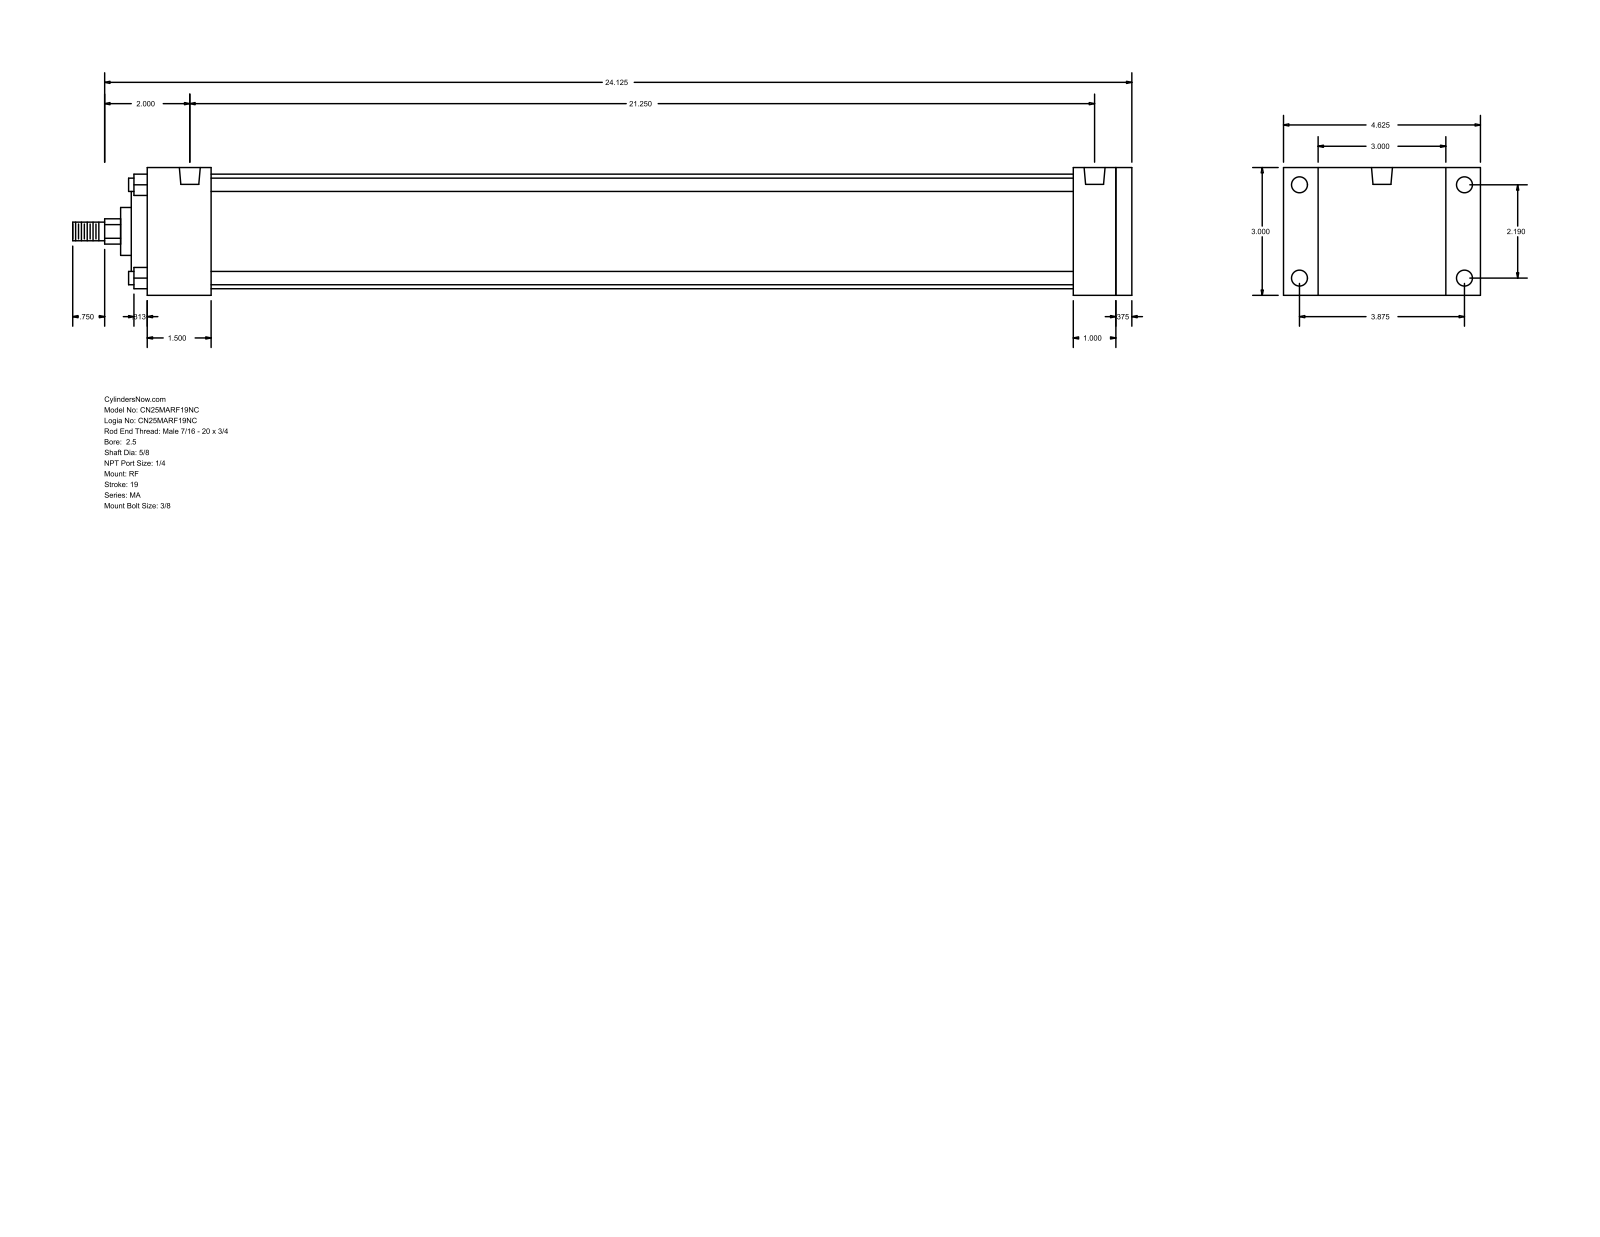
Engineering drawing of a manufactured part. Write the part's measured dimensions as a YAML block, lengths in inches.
part_name: "MA_RF__0250_0.625"
step_written_by: "GSSL Pune (CONFIG_CONTROL_DESIGN)"
units: inches
bodies: {solids: 0, faces: 94, planar: 65, cylindrical: 29, other: 0}
overall_size: [24.875, 4.625, 3]
round_holes:
  - {diameter: 0.313, count: 4}
  - {diameter: 0.375, count: 4}
  - {diameter: 0.492, count: 2}
round_bosses_or_shafts:
  - {diameter: 0.313, count: 4}
  - {diameter: 2.69, count: 1}
  - {diameter: 2, count: 1}
  - {diameter: 1.125, count: 1}
  - {diameter: 0.625, count: 1}
  - {diameter: 0.437, count: 1}
partial_cylinders:
  - {radius: 0.297, count: 1}
face_to_face_distances: [3, 23.125, 0.375, 22.75, 1, 1.5, 21.75, 20.25, 21.25, 21.625]
hole_center_spacings: [2.19, 3.875, 4.451, 21.25]
